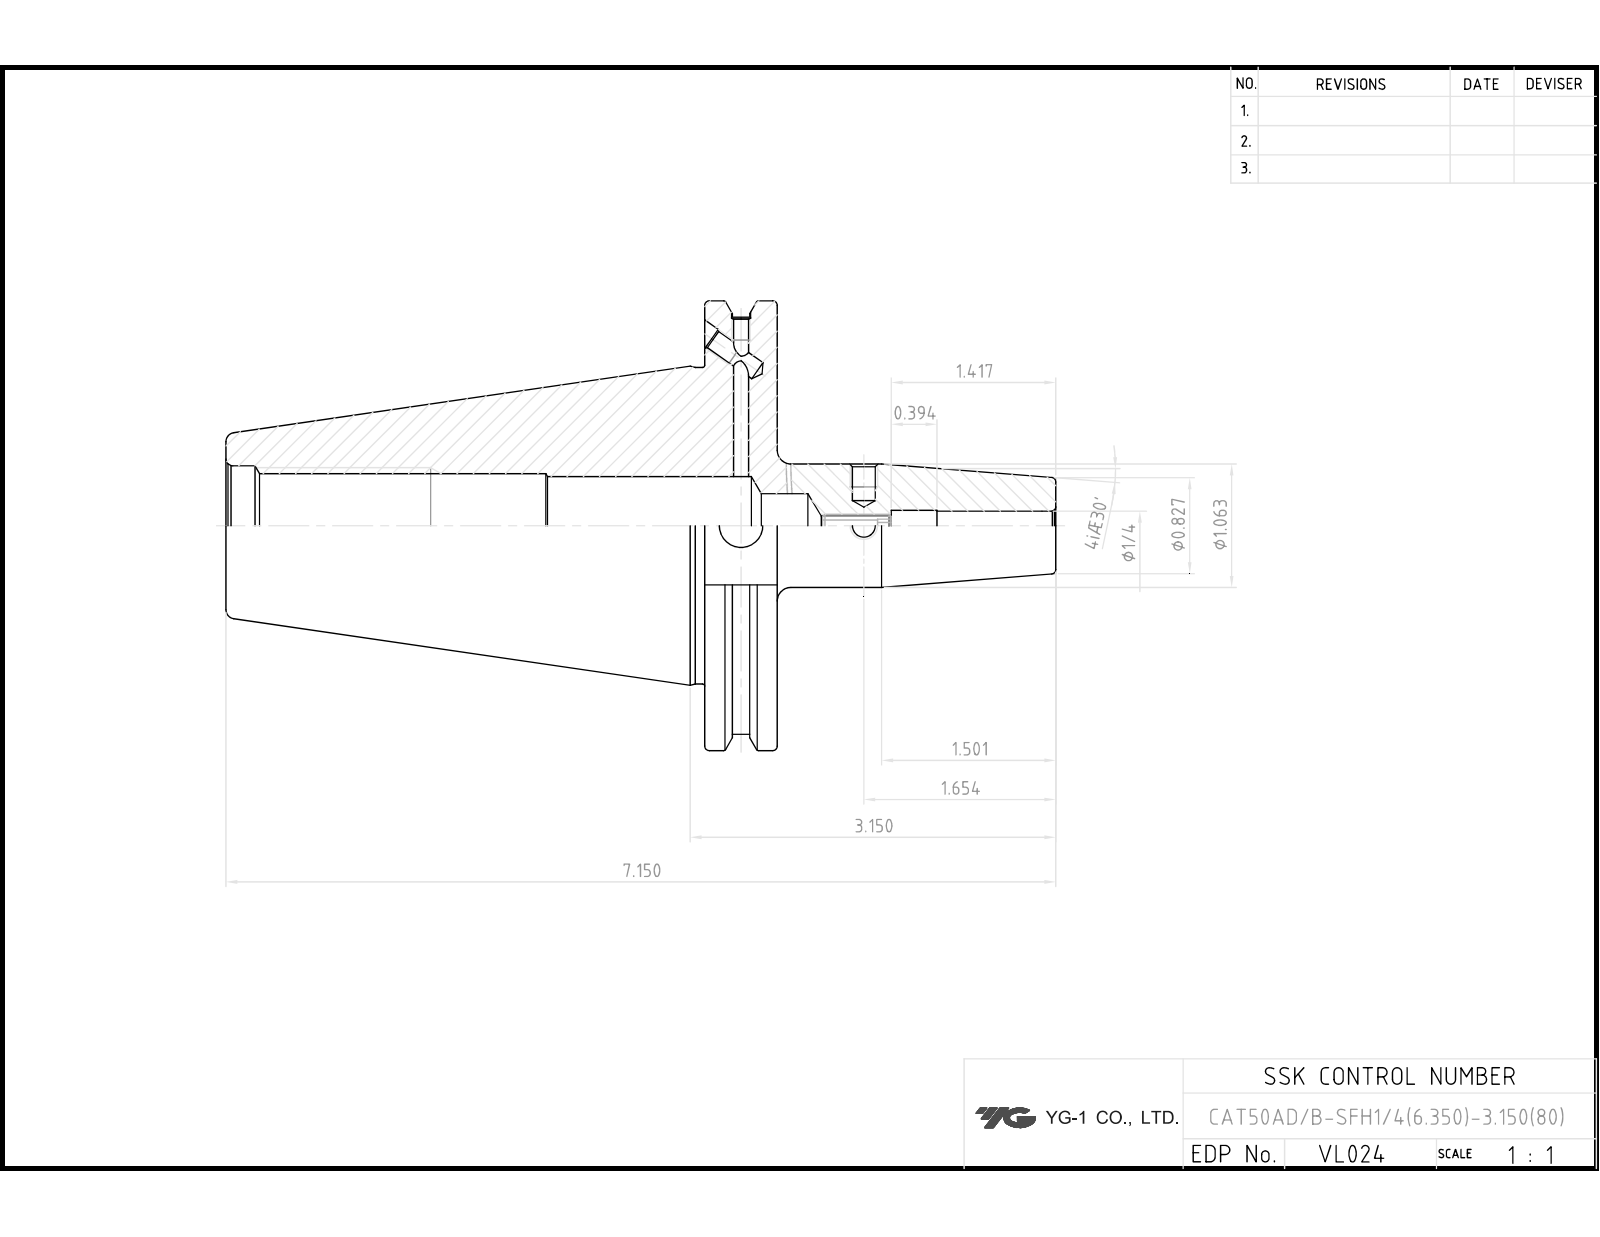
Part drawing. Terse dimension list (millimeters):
name: LO-CAT50ADB-SFH6.35-80
written by: Autodesk Inventor 2025 (AUTOMOTIVE_DESIGN)
unit: mm
bodies: 1 solid, 84 faces (37 planar, 26 cylindrical, 21 other)
size: 181.6 × 98.42 × 94.69
volume: 348 128 mm³; area: 50 644 mm²
holes: 3× ⌀4.13, 2× ⌀3.24, 2× ⌀4.2, 2× ⌀5, 1× ⌀6.35, 1× ⌀7.55, 1× ⌀9.53, 1× ⌀21.97, 1× ⌀26.2
bosses: 1× ⌀98.42, 1× ⌀91.29, 1× ⌀69.25, 1× ⌀27
face distances: 15.88, 104.77, 120.65, 73.03, 25.9, 181.6, 76.83, 60.95, 110.82, 6.05
